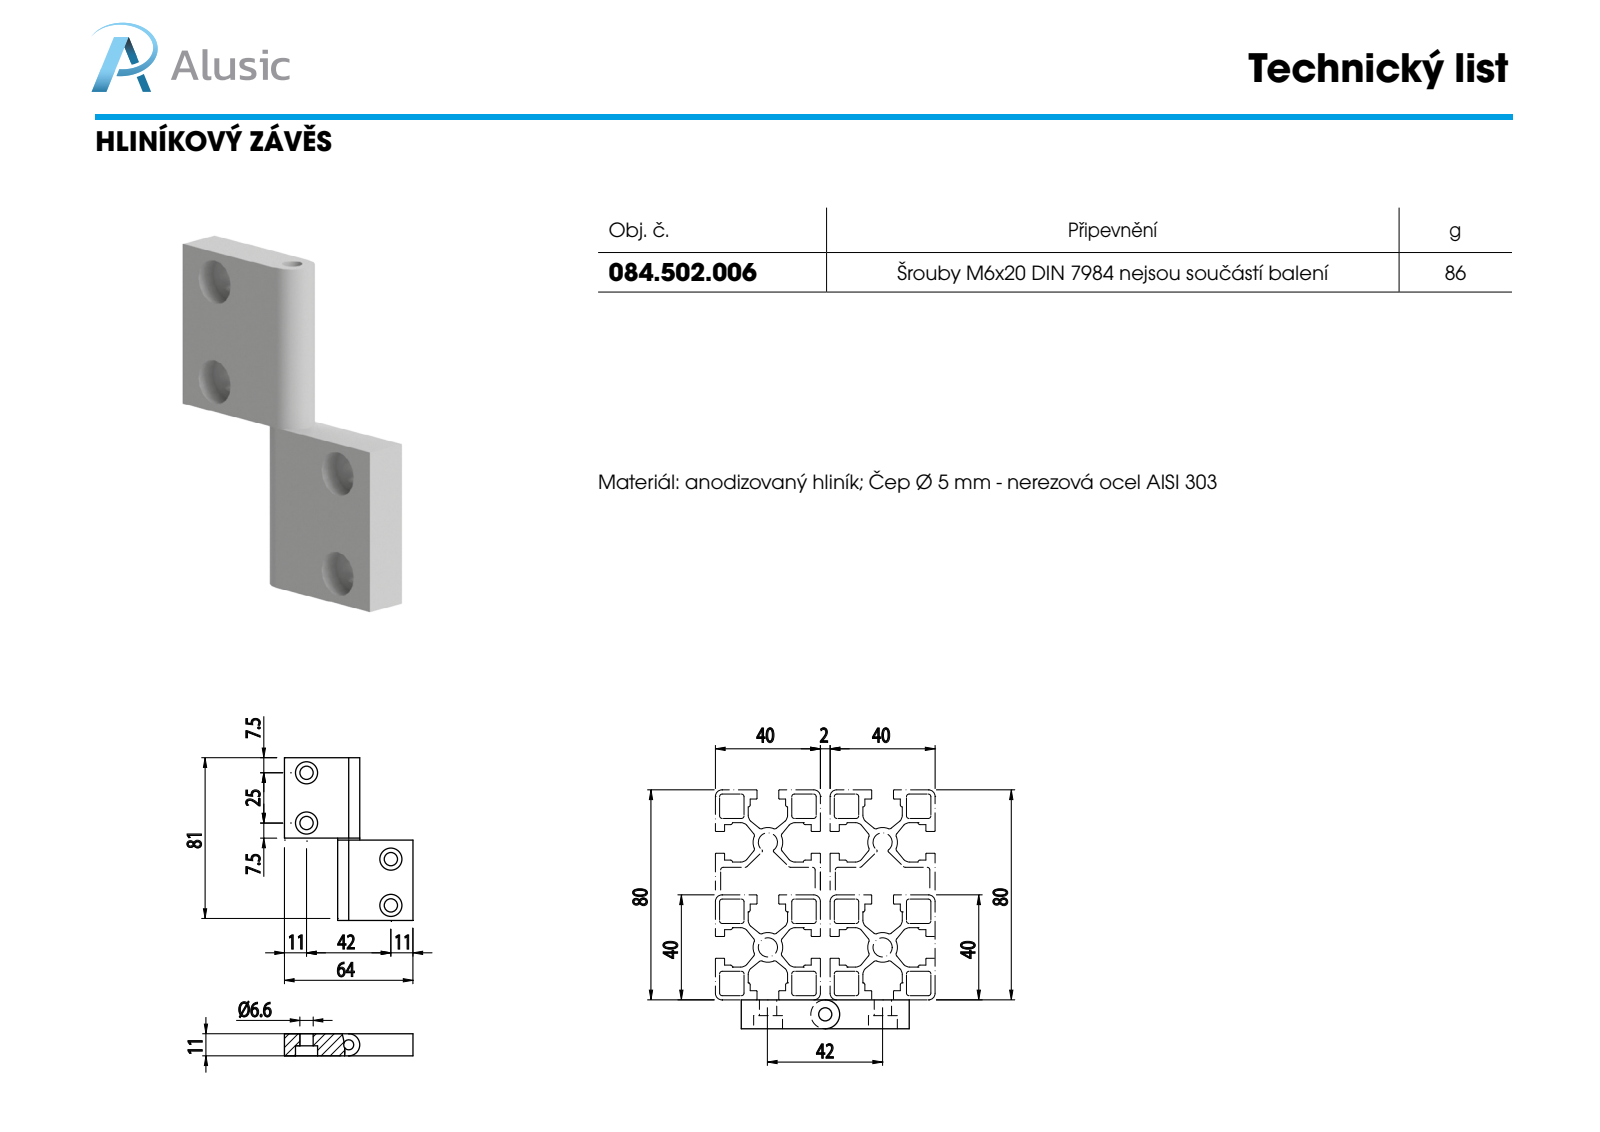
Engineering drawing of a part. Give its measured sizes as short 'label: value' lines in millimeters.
name: 084.502.006; 084.502.000 ALETTE_ALETTA 4
written by: SolidWorks 2012 (CONFIG_CONTROL_DESIGN)
unit: mm
bodies: 2 solids, 36 faces (14 planar, 22 cylindrical, 0 other)
size: 80 × 64 × 11
volume: 27 669 mm³; area: 11 074 mm²
holes: 4× ⌀6.6, 4× ⌀11, 1× ⌀5
bosses: 1× ⌀11
face distances: 11, 40, 64, 80, 6, 5
hole spacings: 25, 58, 44.6, 77.39
